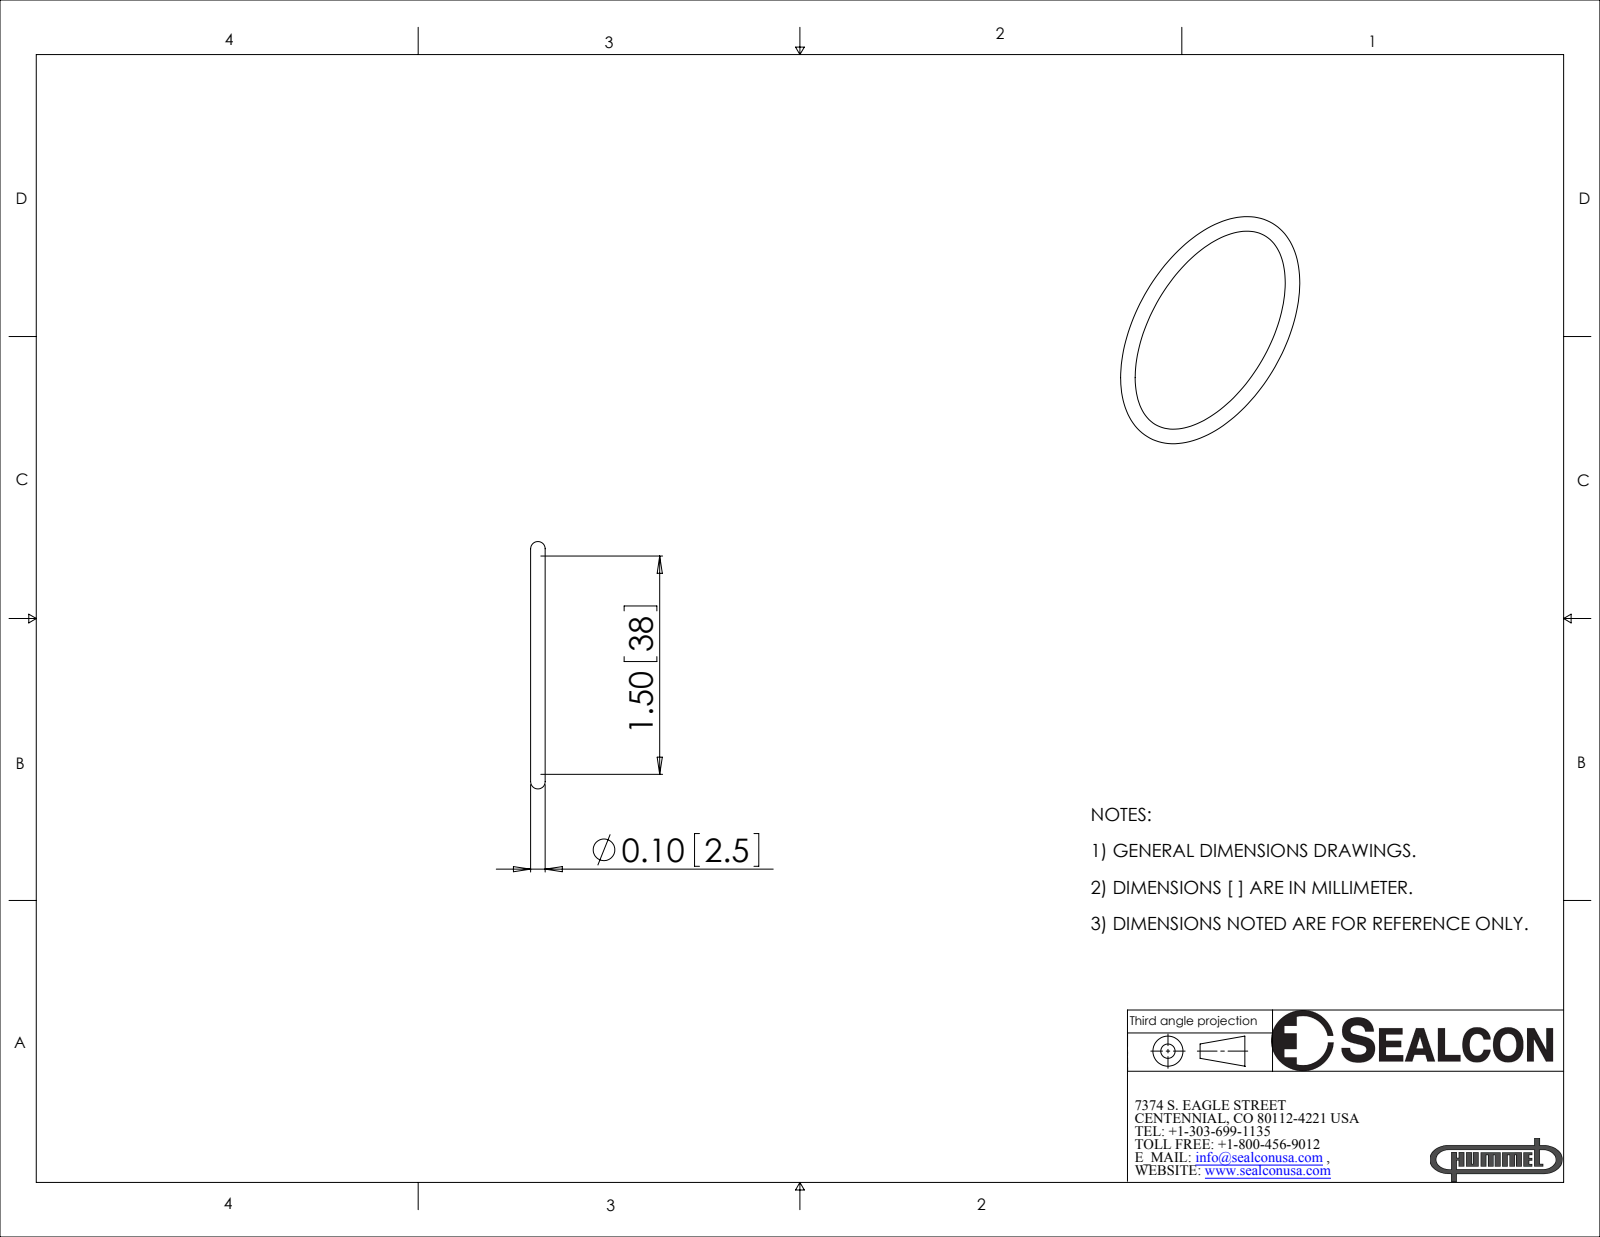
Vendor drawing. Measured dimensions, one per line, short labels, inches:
name: OR-54-SI
written by: SolidWorks 2008 (CONFIG_CONTROL_DESIGN)
unit: in
bodies: 1 solid, 4 faces (0 planar, 0 cylindrical, 4 other)
size: 1.7 × 1.7 × 0.1
volume: 0.039 in³; area: 1.579 in²
